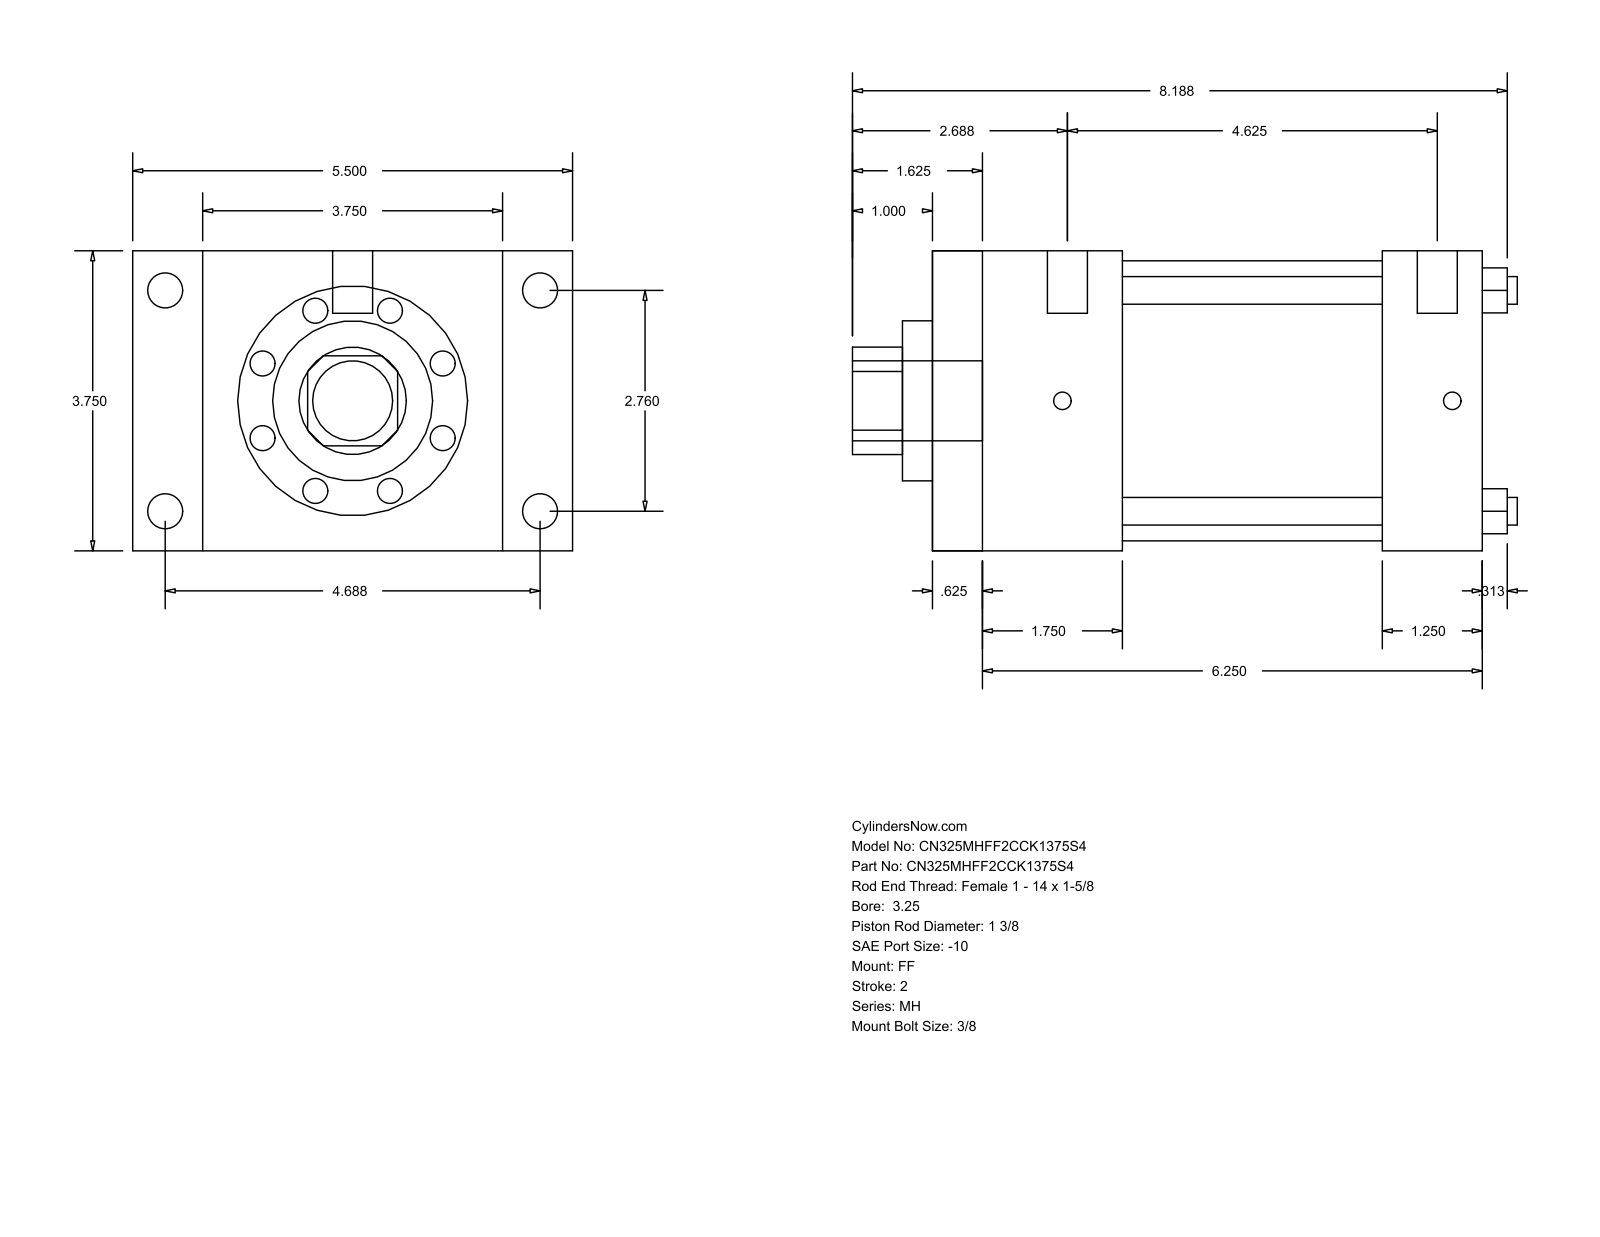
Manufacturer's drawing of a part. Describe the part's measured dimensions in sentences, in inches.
The part is named "MH_FF__0325_1.375". Its 3-D file was written by "GSSL Pune (CONFIG_CONTROL_DESIGN)". It is 0 solids with 92 faces: 64 planar, 28 cylindrical and 0 other. Overall it measures 8.313 by 5.5 by 3.75 inches. Round holes: 4 of diameter 0.345, 1 of diameter 1.375, 1 of diameter 2, 1 of diameter 3.5. Round bosses or shafts: 4 of diameter 0.438, 4 of diameter 0.219, 2 of diameter 0.5, 1 of diameter 1. Partial cylindrical surfaces (rounded edges, fillets, slot ends): 1 of radius 0.672. The main face-to-face distances are 3.75, 6.875, 0.625, 6.25, 0.875, 4.625, 5.625, 5, 1.25, 2.375. The hole center spacings are 1.952, 2.76, 3.903.
